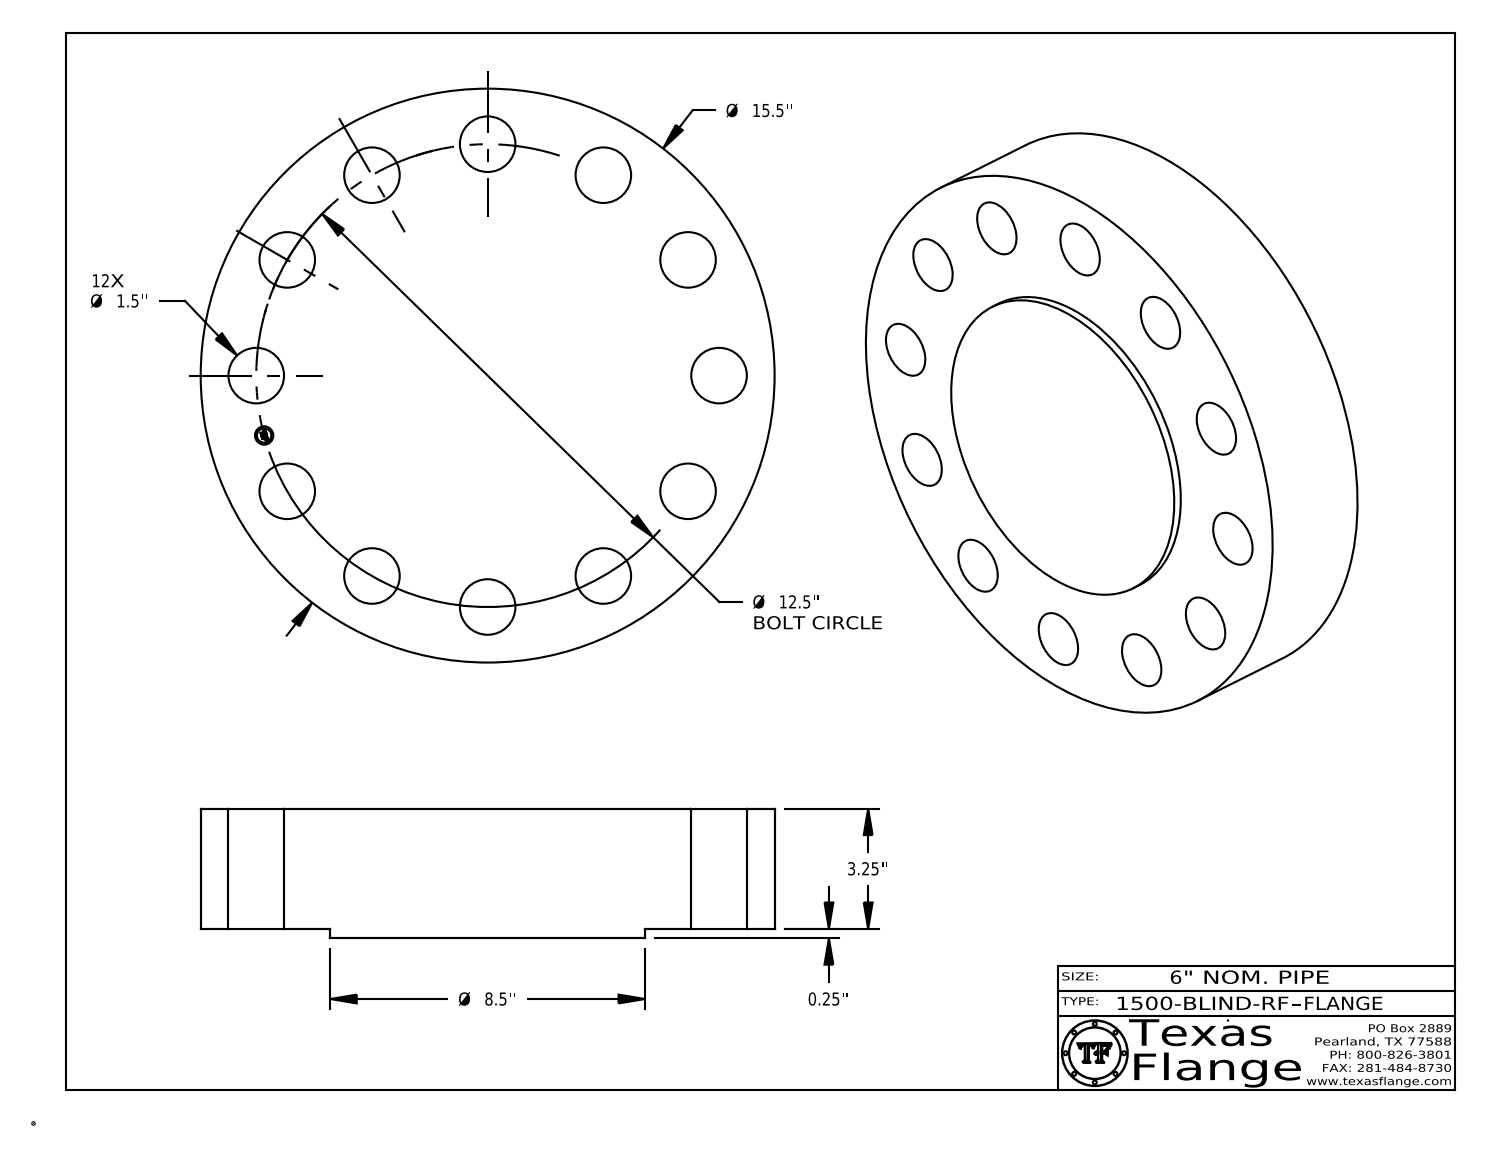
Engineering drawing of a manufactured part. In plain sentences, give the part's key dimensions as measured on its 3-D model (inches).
The part is named "1500-BLIND-RF". Its 3-D file was written by "CATIA V5 STEP AP214 (AUTOMOTIVE_DESIGN)". It is 1 solid with 416 faces: 368 planar, 48 cylindrical and 0 other. Overall it measures 15.5 by 15.5 by 3.5 inches. Its volume is 558.5 cubic inches and its surface area 683.8 square inches. Round holes: 12 of diameter 1.5, 1 of diameter 0.495. Round bosses or shafts: 8 of diameter 0.03, 1 of diameter 15.5, 1 of diameter 8.5, 1 of diameter 0.39. The main face-to-face distances are 3.25, 0.25, 3.5, 3.485, 3.235, 0.015, 0.148, 0.144, 0.027, 0.096. The hole center spacings are 8.839, 3.235, 6.25, 10.826, 12.074, 12.5, 3.235, 6.25.
